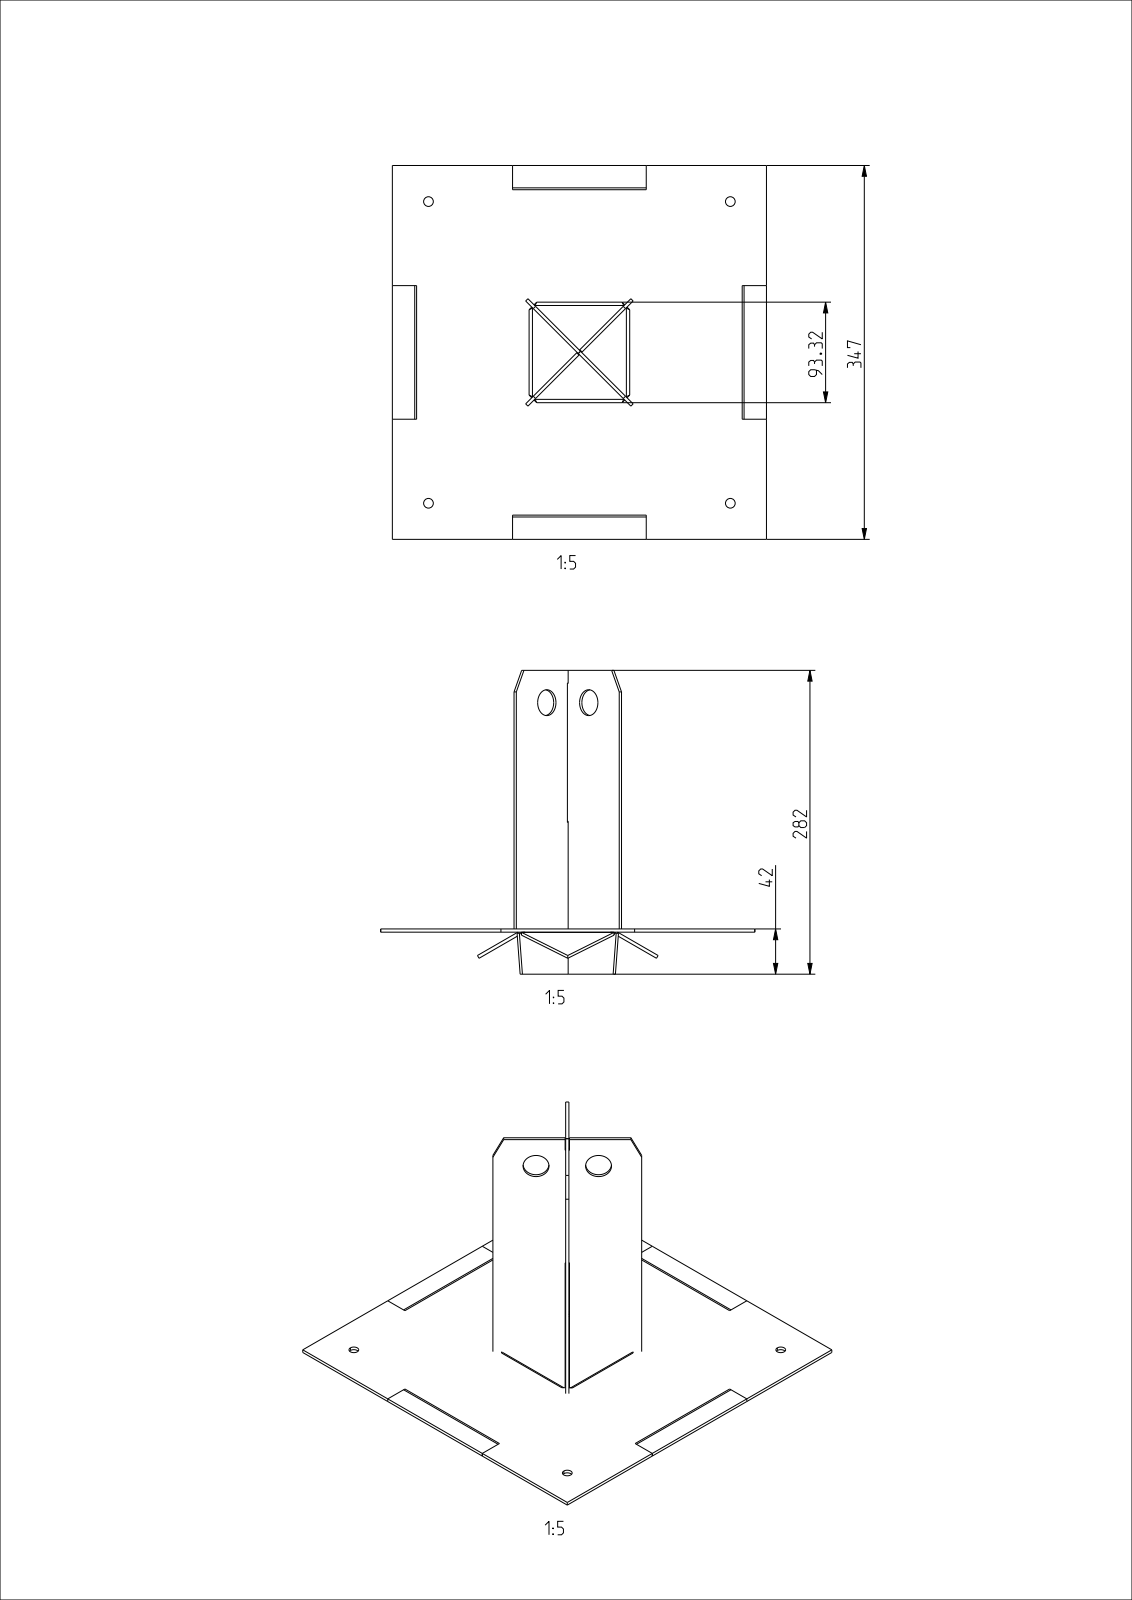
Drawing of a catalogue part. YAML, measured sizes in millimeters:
part_name: "47650-M; 47648-M; 47649-M; 47653-M_ASM"
step_written_by: "CREO PARAMETRIC BY PTC INC, 2022281 (AUTOMOTIVE_DESIGN)"
units: millimeters
bodies: {solids: 3, faces: 154, planar: 114, cylindrical: 24, other: 16}
overall_size: [347, 347, 282]
volume: 581357
surface_area: 401490
round_holes:
  - {diameter: 9, count: 4}
  - {diameter: 24, count: 4}
partial_cylinders:
  - {radius: 0.1, count: 4}
  - {radius: 3.1, count: 4}
face_to_face_distances: [3, 67.49, 70.49, 347, 3.5, 66.99, 70.99, 0.5, 137.98, 4]
hole_center_spacings: [280, 58.01, 395.98]
